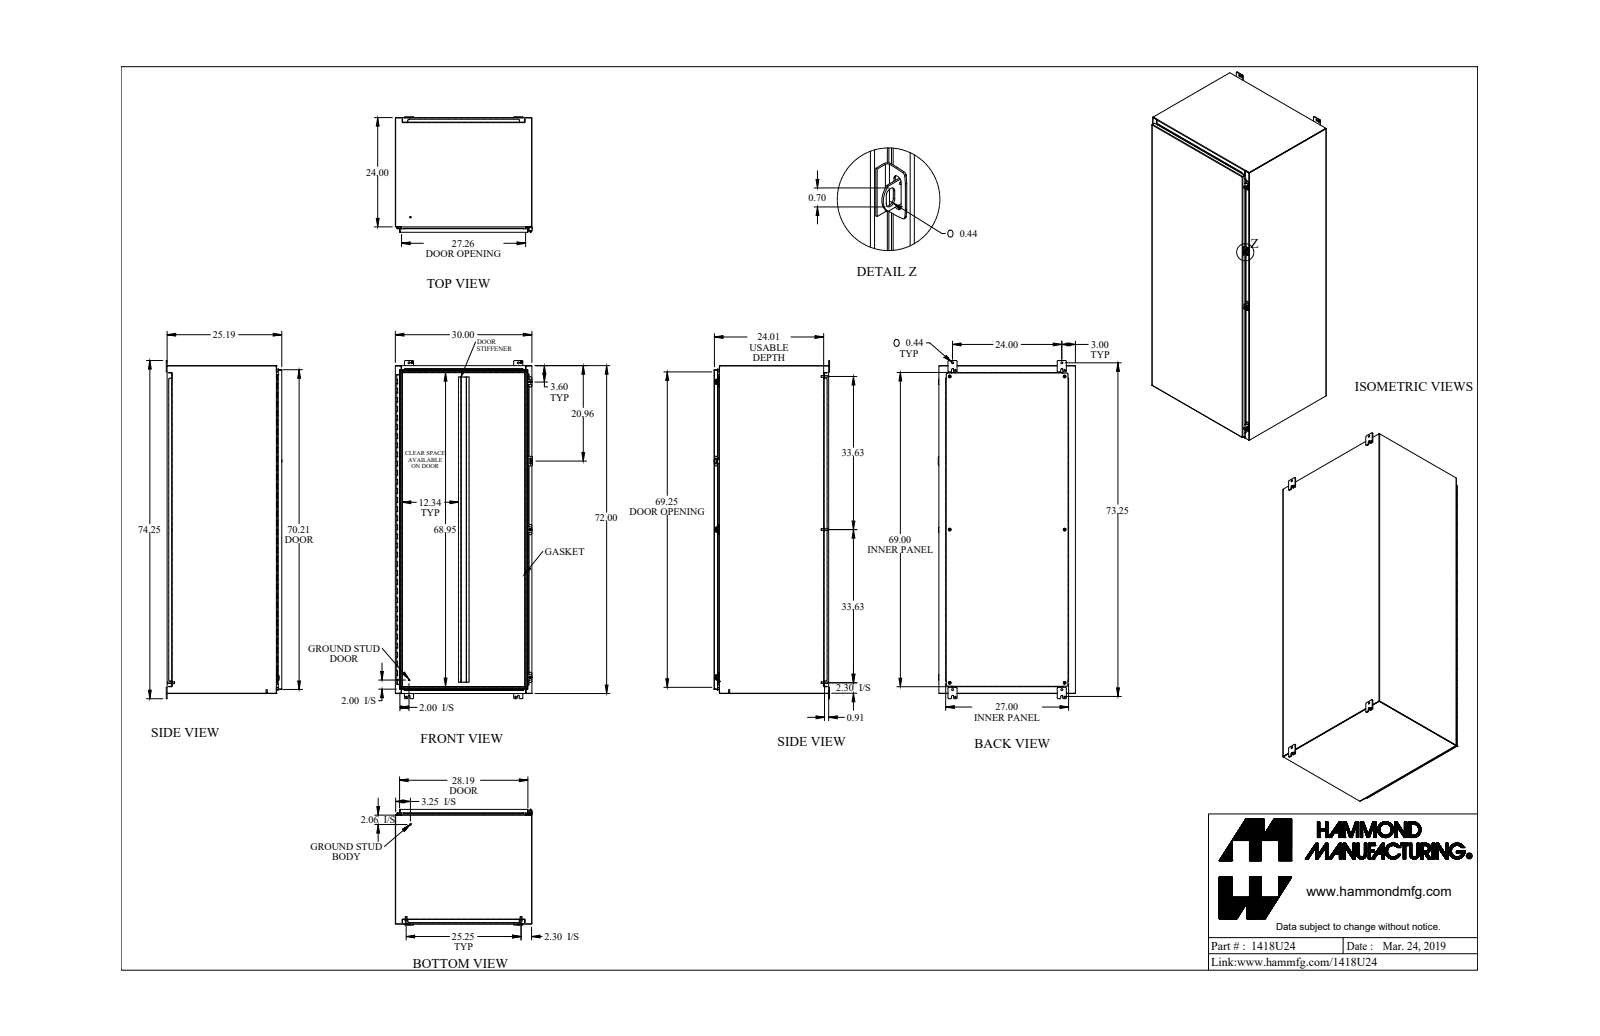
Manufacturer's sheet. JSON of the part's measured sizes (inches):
{"part_name": "1418U24_Default", "step_written_by": "SolidWorks 2019 (CONFIG_CONTROL_DESIGN)", "units": "inches", "bodies": {"solids": 50, "faces": 1846, "planar": 1008, "cylindrical": 778, "other": 60}, "overall_size": [74.25, 30.128, 25.437], "volume_in3": 957.6, "surface_area_in2": 25053, "round_holes": [[0.304, 12], [0.5, 6], [0.307, 4], [0.313, 4], [0.437, 4], [0.445, 4], [0.213, 3], [0.265, 3], [0.375, 3], [0.11, 1], [0.125, 1]], "round_bosses_or_shafts": [[0.65, 6], [0.375, 6], [0.33, 6], [1, 4], [0.5, 3], [0.39, 3], [0.244, 3], [0.281, 2]], "partial_cylinders_radius": [[0.188, 38], [0.036, 22], [0.108, 22], [0.25, 20], [0.048, 19], [0.143, 19], [0.116, 16], [0.125, 8]], "face_to_face_distances": [0.072, 25.113, 29.928, 25.041, 25.185, 0.095, 24.081, 24.009, 1.032, 1.104], "hole_center_spacings": [24, 6, 12, 18, 30, 36, 33.625, 42]}
